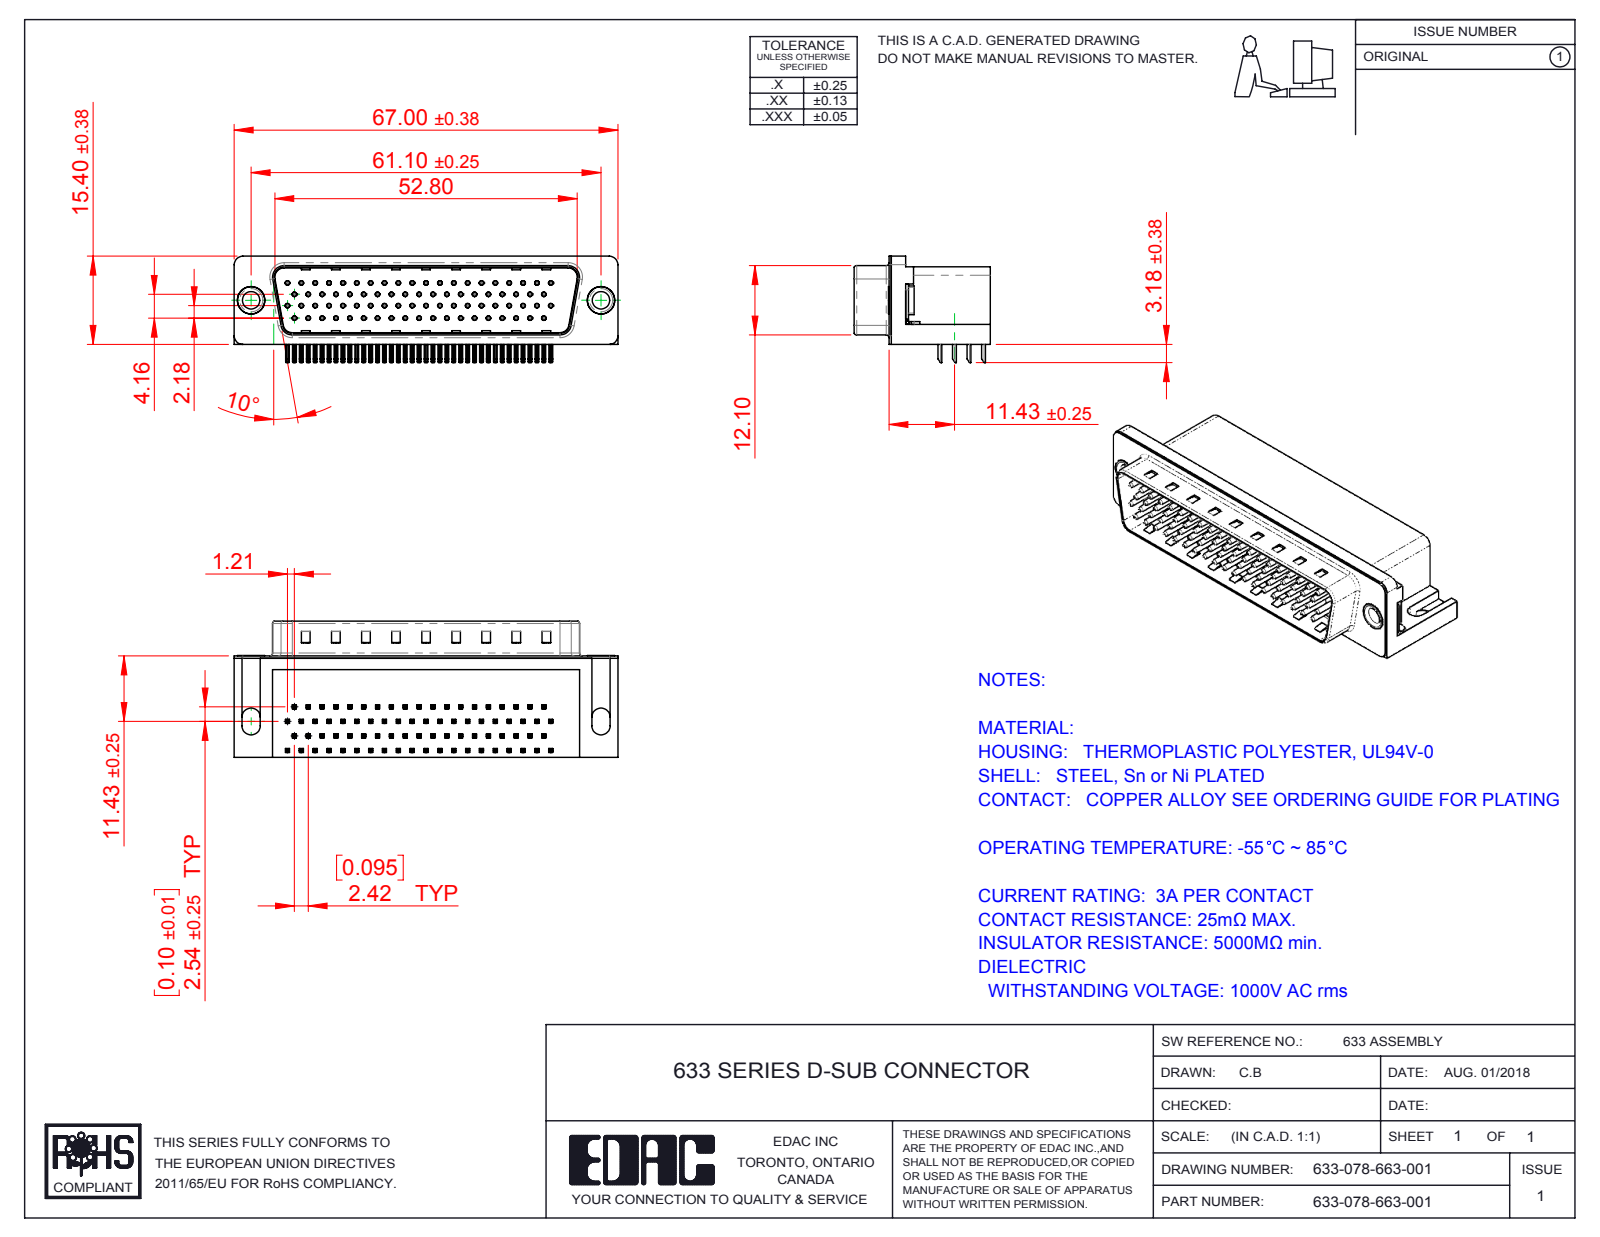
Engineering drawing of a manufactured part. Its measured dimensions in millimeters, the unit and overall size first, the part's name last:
Units: millimetres
Overall size (bounding box): 67 × 23.8 × 18.58
Round holes (diameter × count): ⌀0.35 ×78, ⌀0.8 ×78, ⌀3.05 ×2, ⌀4 ×2, ⌀4.8 ×2, ⌀5 ×2
Round bosses / shafts (diameter × count): ⌀0.75 ×78, ⌀4.9 ×2, ⌀4.75 ×2, ⌀3.85 ×2
Partial cylindrical surfaces — rounded edges, fillets, slot ends (radius × count): R0.25 ×320, R0.12 ×156, R1 ×16, R0.5 ×9, R1.6 ×8, R1.5 ×6, R0.45 ×4, R0.9 ×4
Main face-to-face distances: 0.4, 13.2, 17.3, 11.7, 13.35, 2.05, 13.75, 1.65, 11.9, 1.85
Hole centre spacings: 2.42, 4.84, 7.26, 9.68, 6.26, 7.13, 12.1, 8.62
Volume: 14 553 mm³ · Surface area: 16 106 mm²
Bodies: 84 solids, 6230 faces (3979 planar, 1756 cylindrical, 495 other)
Part name (STEP PRODUCT): 633-078-663-001; 633 Thru Hole Rivet; 633 Shell_78 Contact; 633 Contact Top_78 Contact (+5 more)
STEP written by: SolidWorks 2016 (CONFIG_CONTROL_DESIGN)
